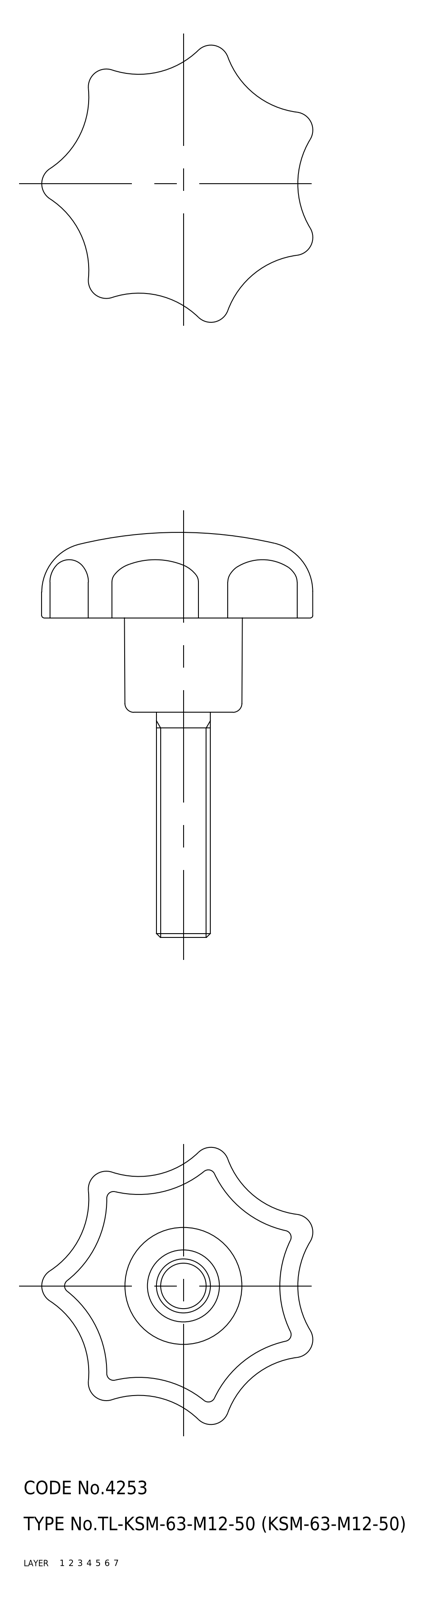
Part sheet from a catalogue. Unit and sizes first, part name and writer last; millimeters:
Units: millimetres
Overall size (bounding box): 90 × 61.62 × 60.28
Volume: 41 899 mm³ · Surface area: 16 659 mm²
Bodies: 2 solids, 100 faces (0 planar, 0 cylindrical, 100 other)
Part name (STEP PRODUCT): screw; knob; KSM_63_M12_50_9877_36
STEP written by: CADfix (AUTOMOTIVE_DESIGN)
